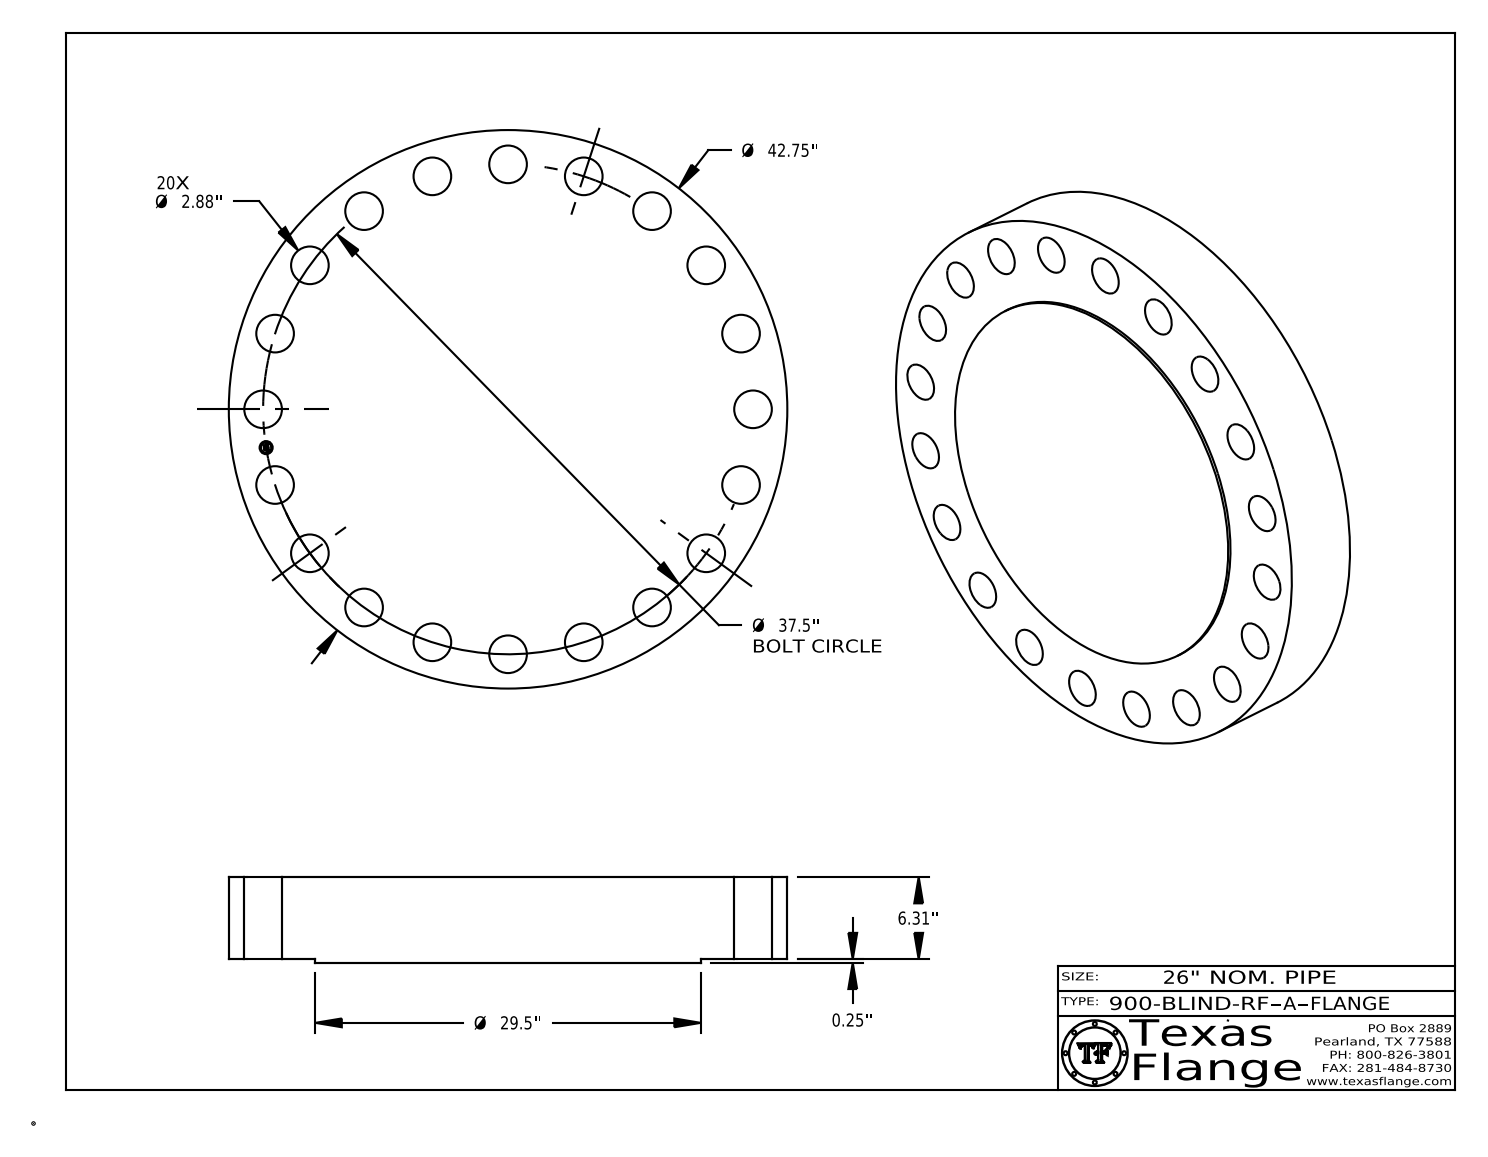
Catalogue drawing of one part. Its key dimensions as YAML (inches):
part_name: "900-BLIND-RF, Series A"
step_written_by: "CATIA V5 STEP AP214 (AUTOMOTIVE_DESIGN)"
units: inches
bodies: {solids: 1, faces: 432, planar: 368, cylindrical: 64, other: 0}
overall_size: [42.75, 42.75, 6.56]
volume: 8406
surface_area: 4623
round_holes:
  - {diameter: 2.88, count: 20}
  - {diameter: 1, count: 1}
round_bosses_or_shafts:
  - {diameter: 0.061, count: 8}
  - {diameter: 42.75, count: 1}
  - {diameter: 29.5, count: 1}
  - {diameter: 0.788, count: 1}
face_to_face_distances: [6.56, 0.25, 6.31, 0.015, 6.545, 6.295, 0.298, 0.293, 0.054, 0.193]
hole_center_spacings: [5.866, 11.588, 17.024, 22.042, 33.413, 35.665, 37.038, 26.517]
